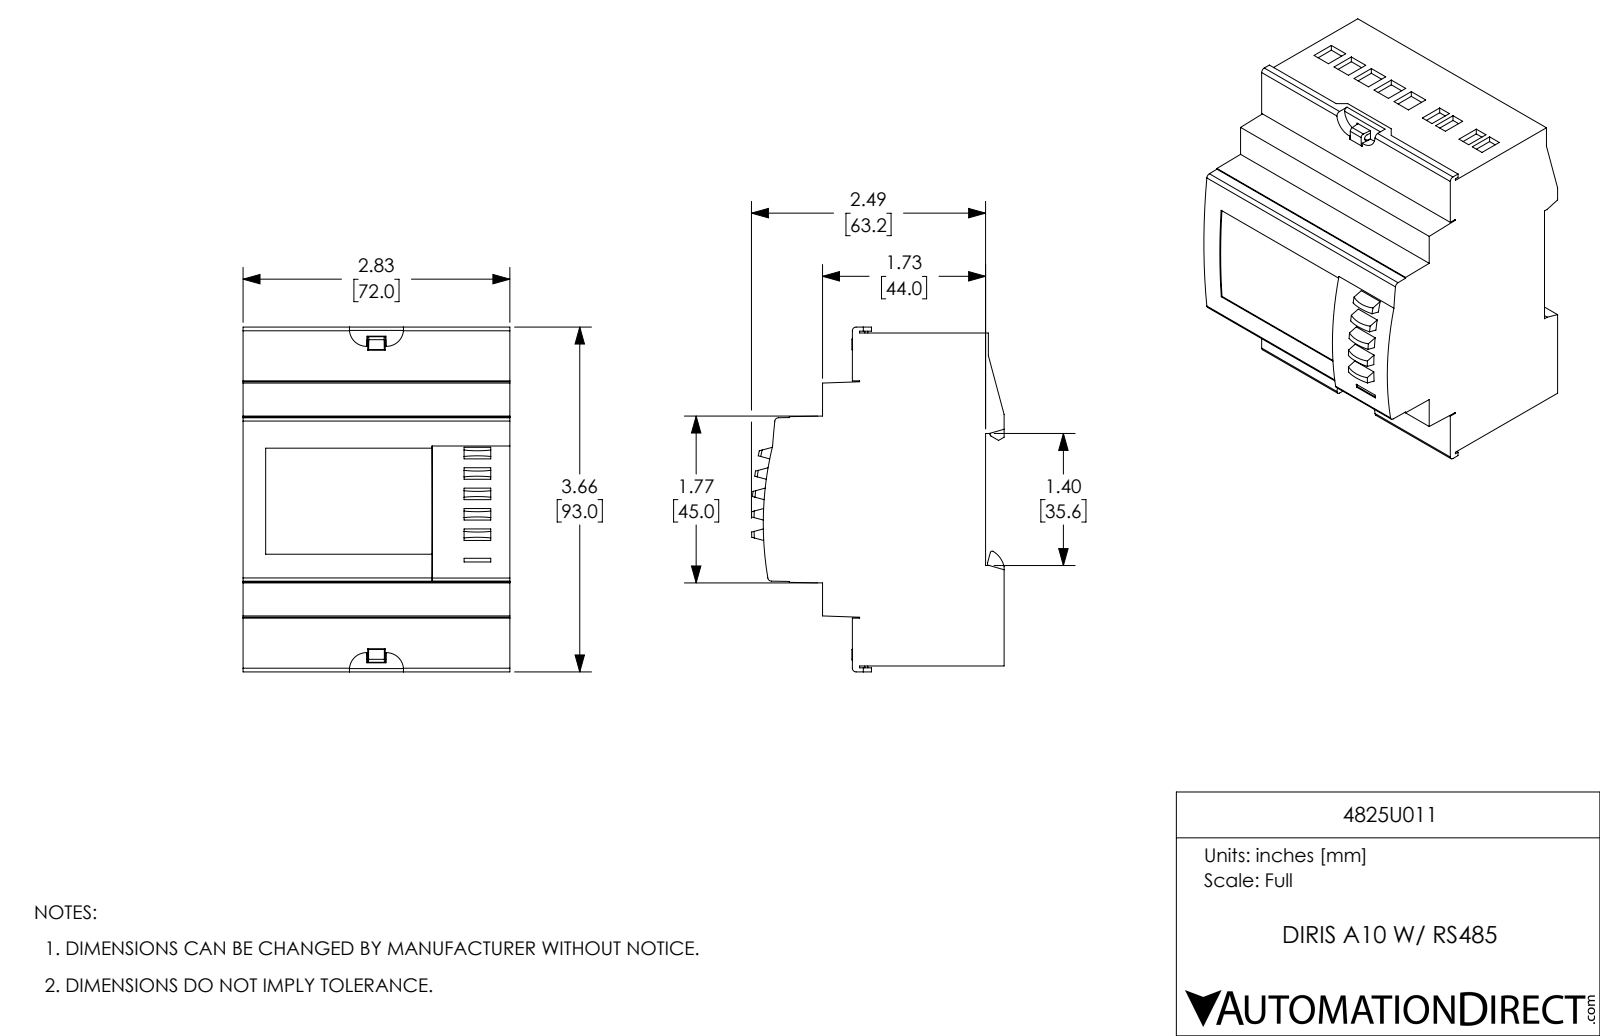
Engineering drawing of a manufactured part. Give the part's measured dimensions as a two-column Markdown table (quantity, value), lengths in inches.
| quantity | value |
| --- | --- |
| part name | 4825U011 |
| STEP written by | SolidWorks 2017 (AUTOMOTIVE_DESIGN) |
| units | inches |
| bodies | 1 solid, 532 faces (373 planar, 128 cylindrical, 31 other) |
| overall size | 3.661 × 2.835 × 2.684 |
| volume | 19.95 in³ |
| surface area | 56.72 in² |
| round holes (diameter × count) | 0.198 × 7, 0.161 × 6, 0.198 × 4 |
| round bosses / shafts (diameter × count) | 0.187 × 11, 0.15 × 6 |
| partial cylindrical surfaces (radius × count) | 0.039 × 5, 0.035 × 4, 0.129 × 4, 0.129 × 4, 0.181 × 4, 0.22 × 4, 0.26 × 4, 0.3 × 4 |
| main face-to-face distances | 2.835, 3.535, 0.197, 1.415, 1.612, 1.929, 1.732, 0.317, 0.03, 0.167 |
| hole center spacings | 0.25, 0.3, 0.5, 0.2, 0.6, 0.75, 0.55, 0.9 |
